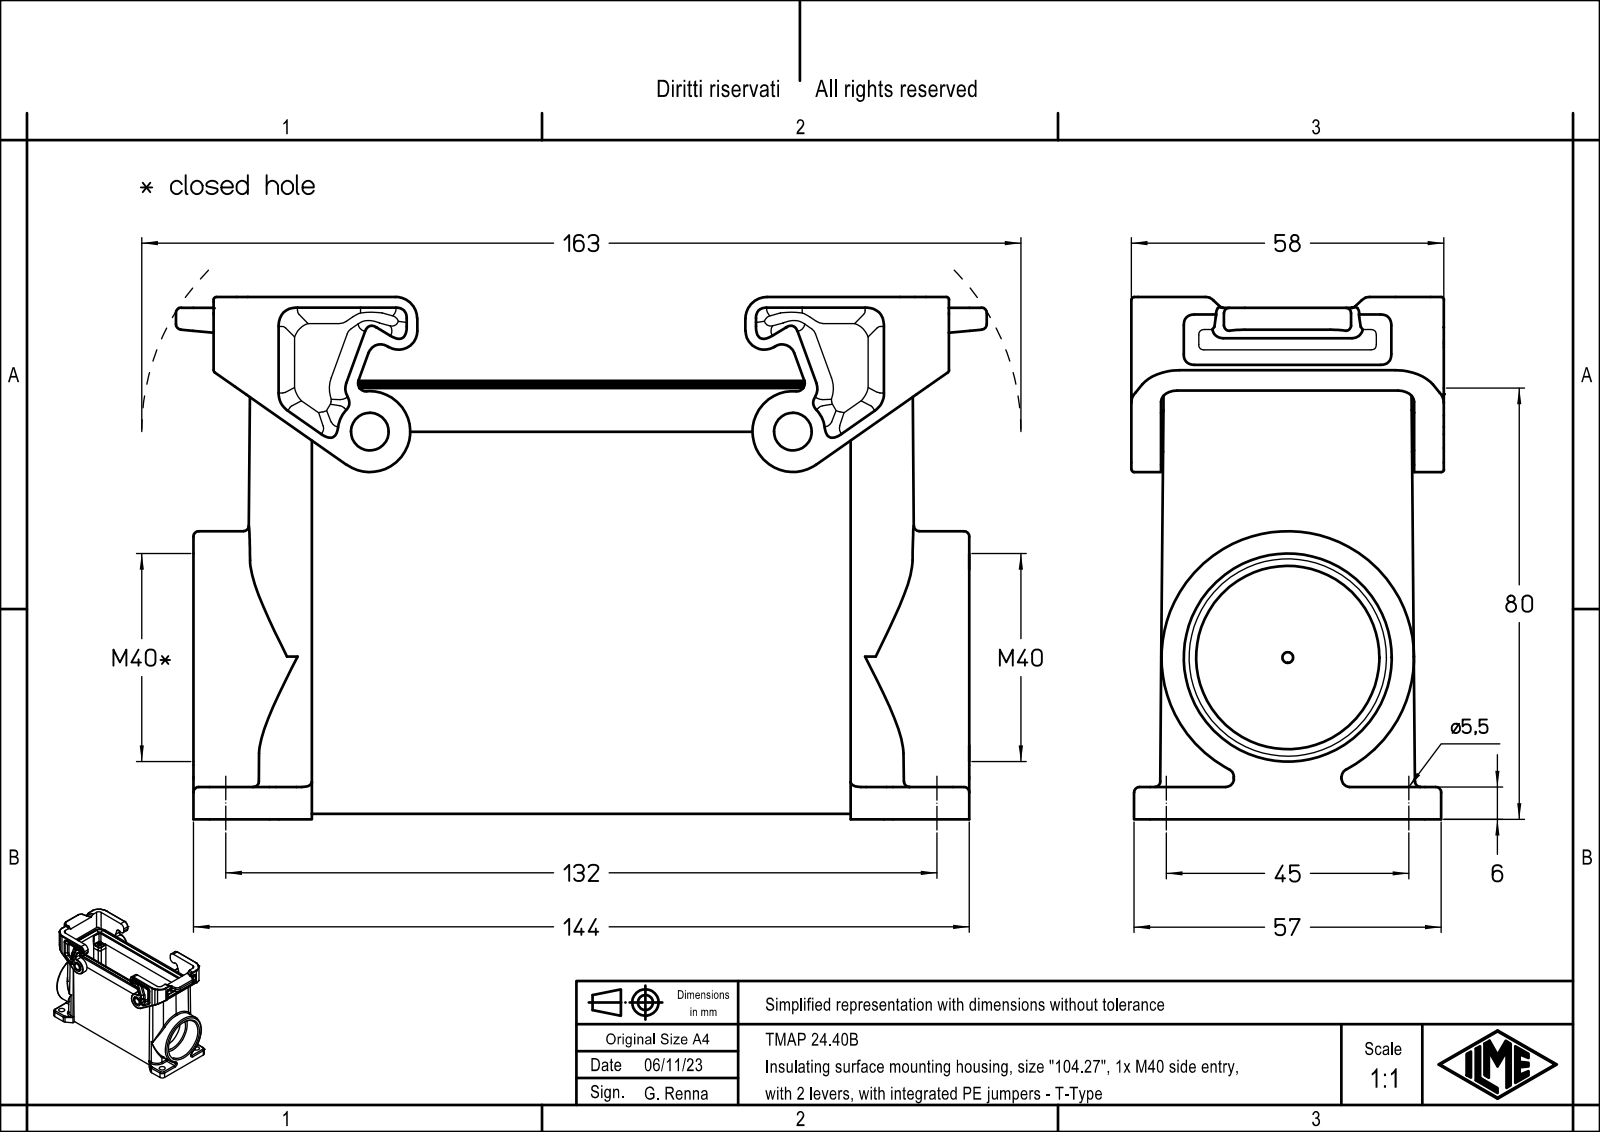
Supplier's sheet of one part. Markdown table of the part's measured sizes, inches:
| quantity | value |
| --- | --- |
| part name | TMAP 24.40B |
| STEP written by | Creo Elements/Direct Modeling 20.1B 02-Apr-2019 (C) Parametric Technology GmbH (AUTOMOTIVE_DESIGN) |
| units | inches |
| bodies | 1 solid, 606 faces (360 planar, 194 cylindrical, 52 other) |
| overall size | 5.925 × 3.815 × 2.283 |
| volume | 12.88 in³ |
| surface area | 133 in² |
| round holes (diameter × count) | 0.138 × 4, 0.217 × 4, 1.339 × 1, 1.52 × 1 |
| round bosses / shafts (diameter × count) | 0.276 × 2, 1.845 × 1 |
| partial cylindrical surfaces (radius × count) | 0.079 × 20, 0.118 × 20, 0.059 × 18, 0.039 × 16, 0.051 × 12, 0.236 × 8, 0.276 × 8, 0.157 × 6 |
| main face-to-face distances | 1.386, 0.217, 0.232, 1.618, 0.039, 0.256, 0.248, 1.602, 0.016, 1.37 |
| hole center spacings | 0.655, 1.521, 4.659, 4.857, 1.063, 1.772, 4.094, 4.23 |
